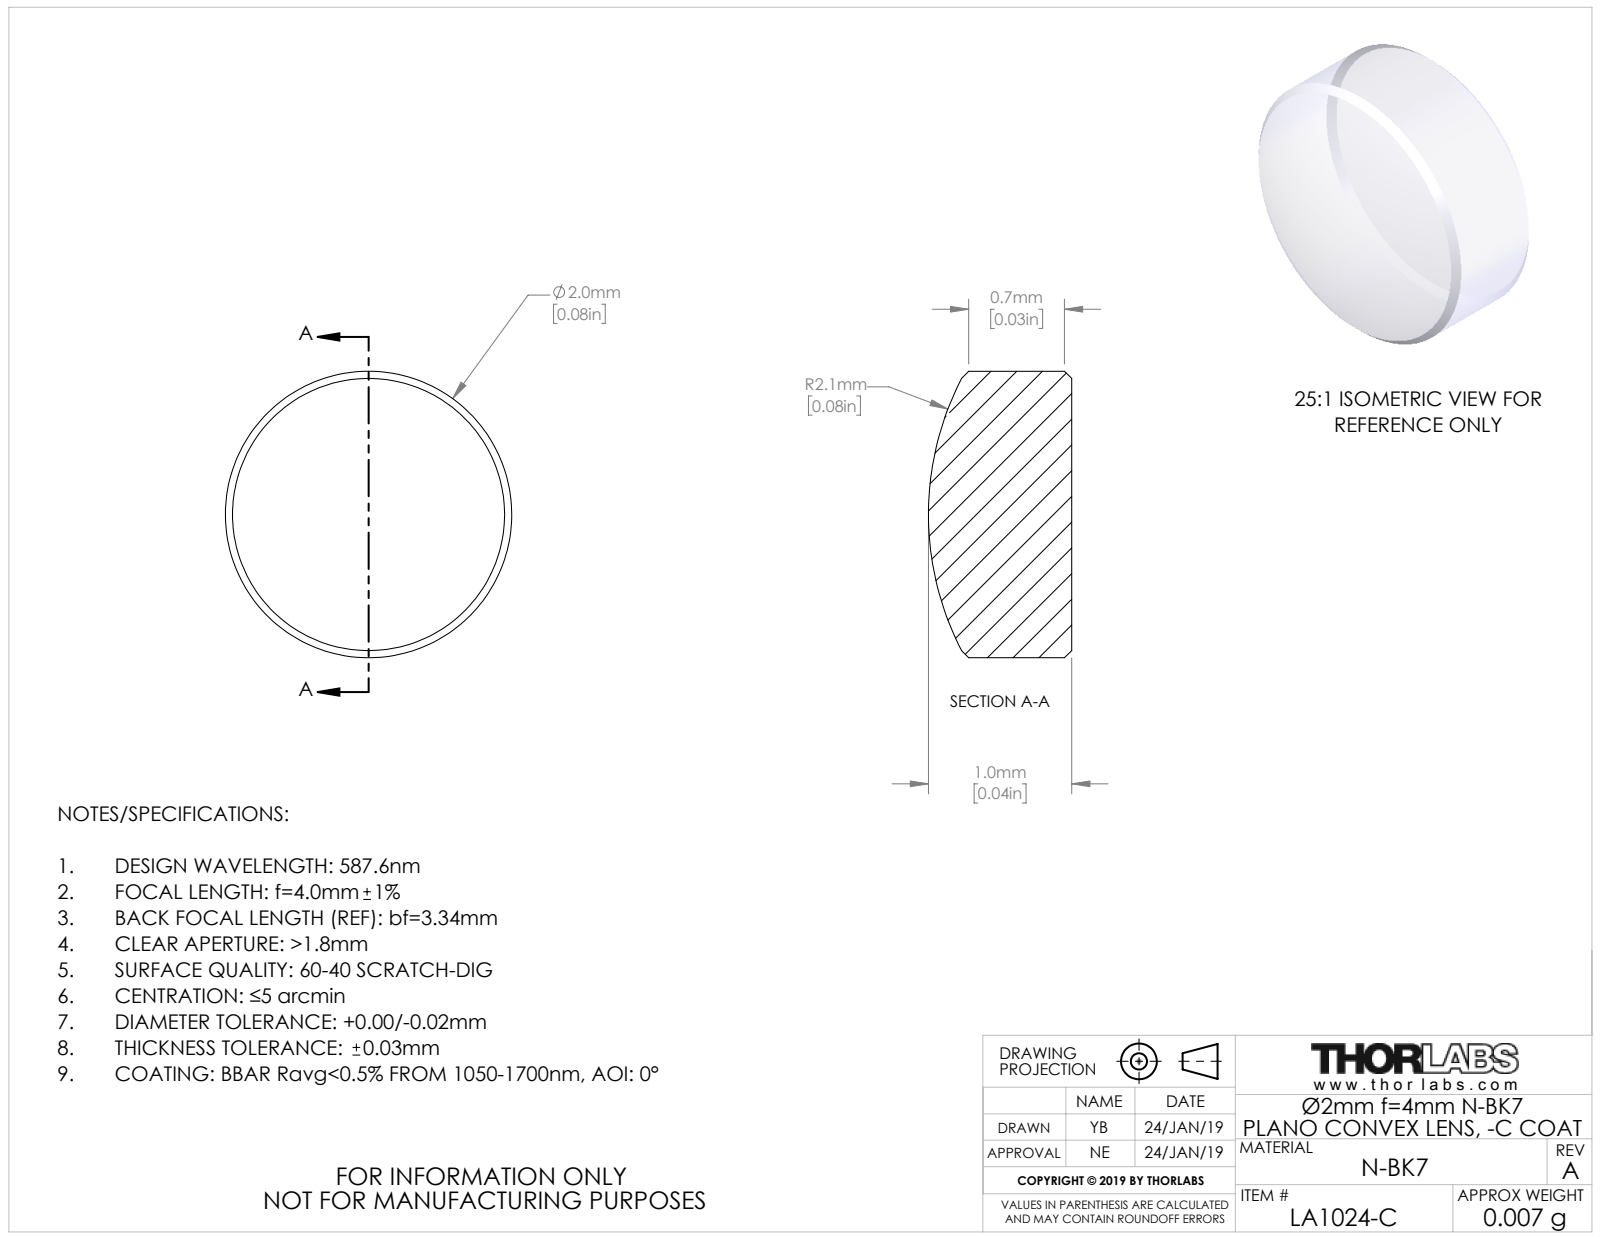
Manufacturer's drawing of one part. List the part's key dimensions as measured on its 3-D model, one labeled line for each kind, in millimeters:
Part name (STEP PRODUCT): TTN162612-E0W
STEP written by: SolidWorks 2018 (CONFIG_CONTROL_DESIGN)
Units: millimetres
Bodies: 1 solid, 9 faces (1 planar, 2 cylindrical, 6 other)
Overall size (bounding box): 2 × 2 × 1
Volume: 3 mm³ · Surface area: 11 mm²
Round bosses / shafts (diameter × count): ⌀2 ×1
